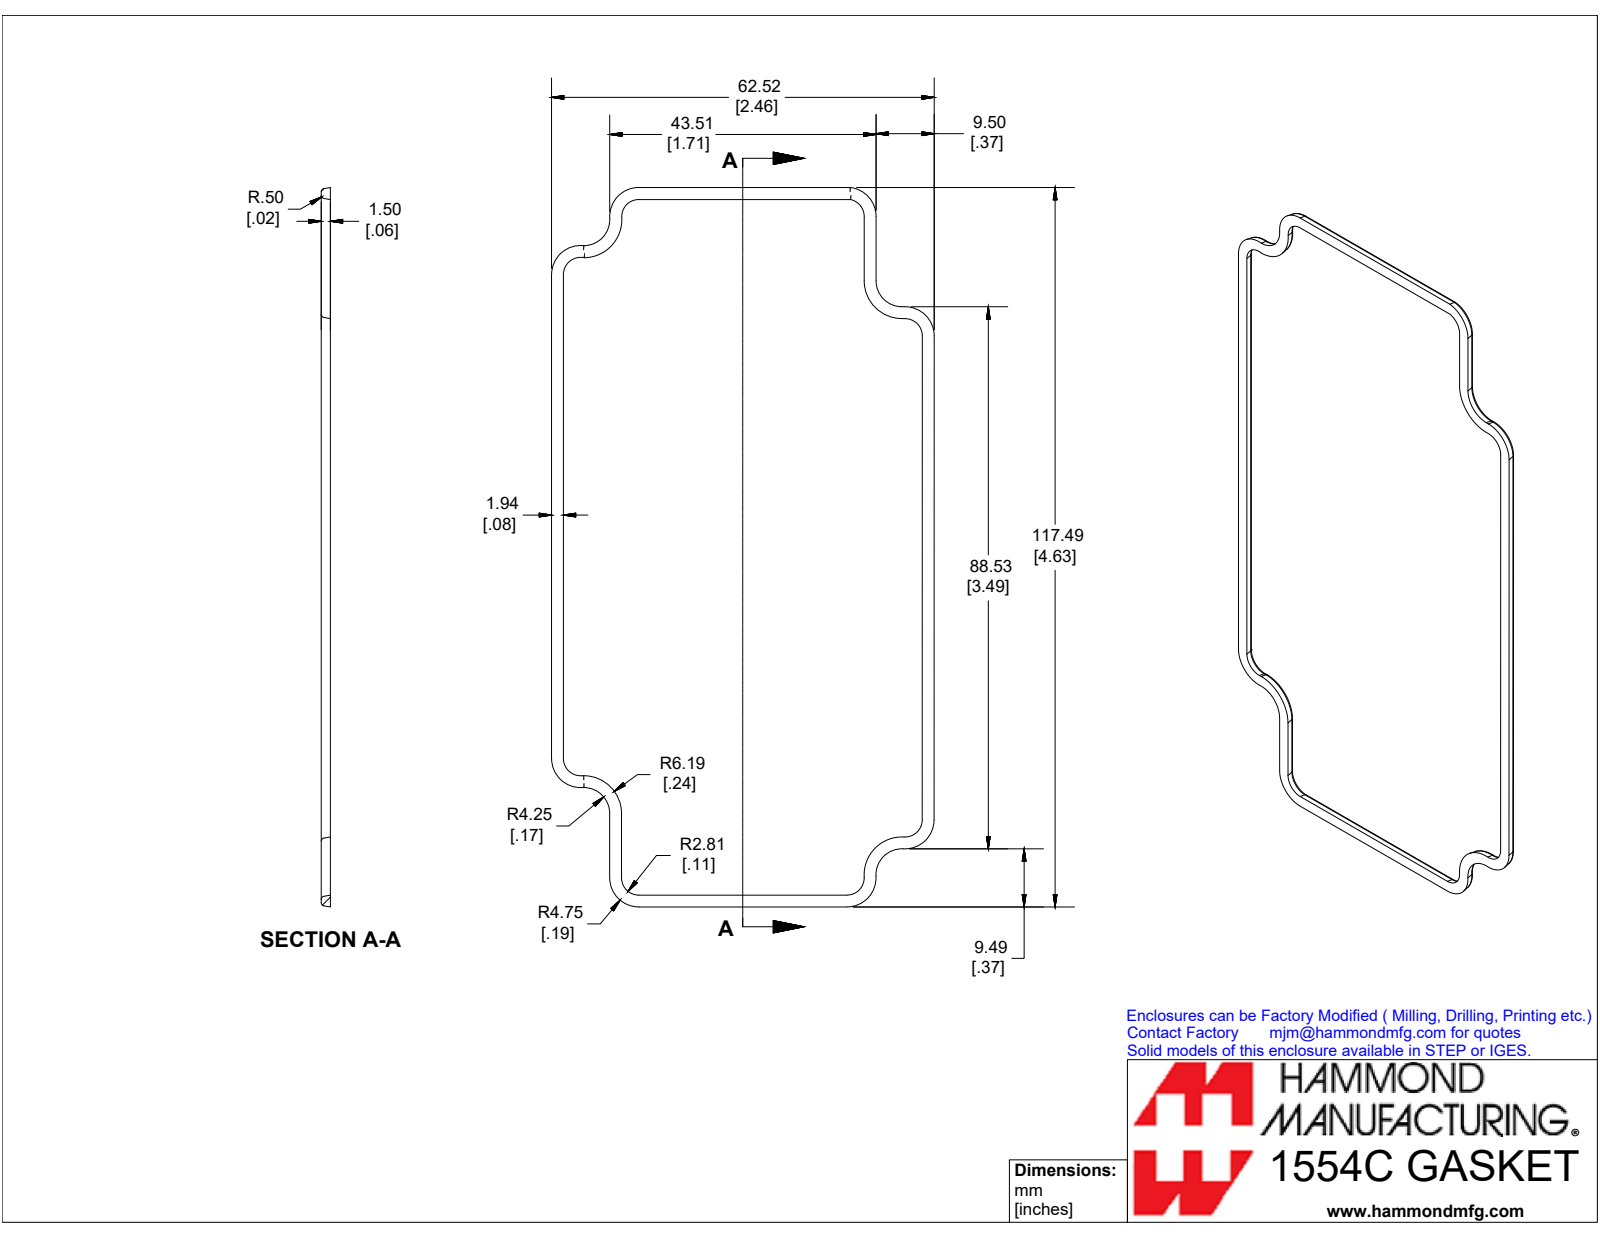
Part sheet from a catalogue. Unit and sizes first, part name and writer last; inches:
Units: inches
Overall size (bounding box): 4.625 × 2.461 × 0.059
Partial cylindrical surfaces — rounded edges, fillets, slot ends (radius × count): R0.02 ×16
Main face-to-face distances: 0.059, 2.35, 0.369, 1.981, 4.48, 4.481, 1.613, 3.726, 0.755, 0.754
Volume: 0.049 in³ · Surface area: 3.134 in²
Bodies: 1 solid, 82 faces (18 planar, 16 cylindrical, 48 other)
Part name (STEP PRODUCT): 1554CGASKET
STEP written by: SolidWorks 2019 (CONFIG_CONTROL_DESIGN)
